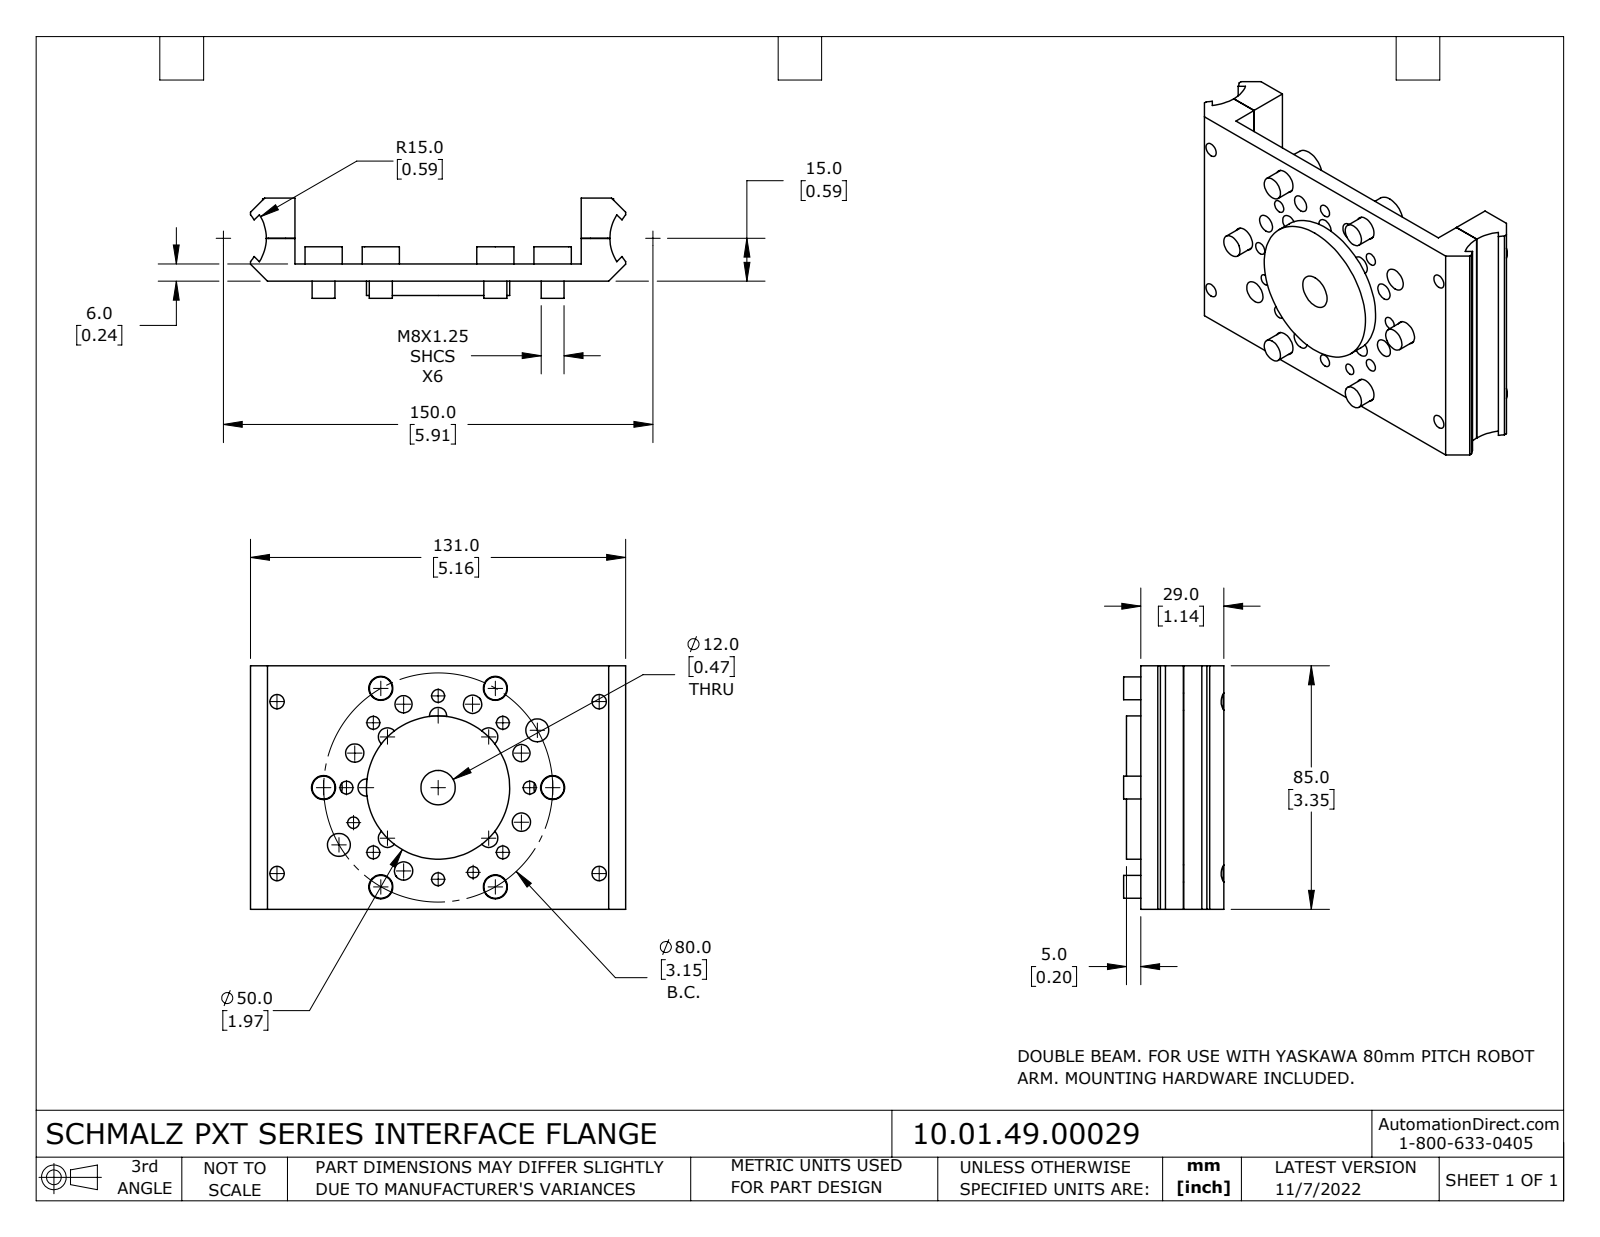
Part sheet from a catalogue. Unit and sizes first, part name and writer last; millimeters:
Units: millimetres
Overall size (bounding box): 131 × 85 × 35
Round holes (diameter × count): ⌀6.4 ×12, ⌀4.5 ×8, ⌀5 ×6, ⌀6 ×6, ⌀8.4 ×6, ⌀5.4 ×4, ⌀6.3 ×4, ⌀10.5 ×4, ⌀4 ×2, ⌀8 ×2, ⌀12 ×1, ⌀16 ×1
Round bosses / shafts (diameter × count): ⌀13 ×6, ⌀8 ×6, ⌀10 ×4, ⌀6 ×4, ⌀50 ×1
Partial cylindrical surfaces — rounded edges, fillets, slot ends (radius × count): R12.5 ×2, R15 ×2
Main face-to-face distances: 6, 100, 11, 5, 20, 8.9, 14.9, 19.9, 17, 9
Hole centre spacings: 43.75, 51.06, 20.17, 23.65, 24.49, 35.67, 40, 59.13
Volume: 119 208 mm³ · Surface area: 54 840 mm²
Bodies: 14 solids, 231 faces (67 planar, 164 cylindrical, 0 other)
Part name (STEP PRODUCT): 10.01.49.00029
STEP written by: SolidWorks 2021 (CONFIG_CONTROL_DESIGN)
